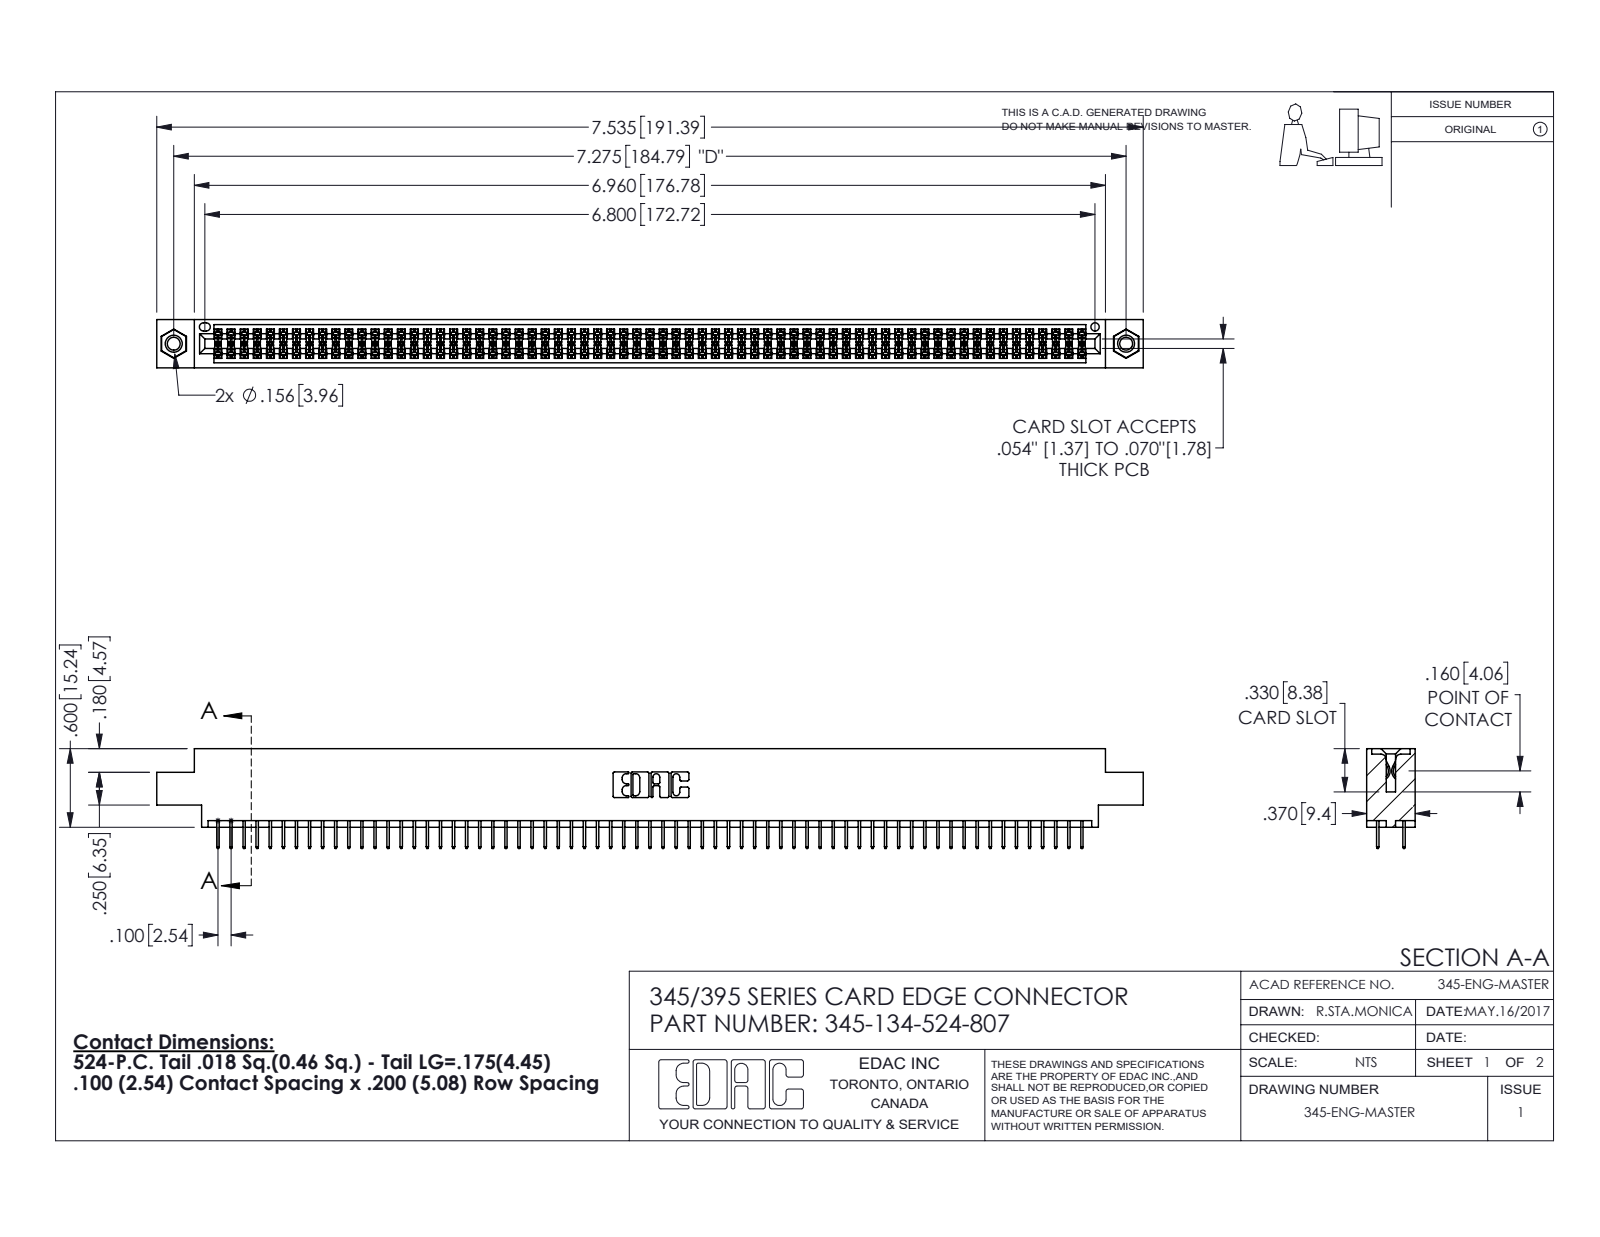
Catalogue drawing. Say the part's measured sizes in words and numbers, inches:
The part is named "345 Part_0.170 Offset - 0.156 Dia-TI; 345-250-001_345-250-005-103; 345-292-001_345-293-124; 345-134-524-807". Its 3-D file was written by "SolidWorks 2016 (CONFIG_CONTROL_DESIGN)". It is 137 solids with 7426 faces: 5342 planar, 2068 cylindrical and 16 other. Overall it measures 7.535 by 0.762 by 0.37 inches. Its volume is 1.129 cubic inches and its surface area 42.56 square inches. Round holes: 2 of diameter 0.098, 2 of diameter 0.125, 2 of diameter 0.156, 1 of diameter 0.064. Round bosses or shafts: 2 of diameter 0.155. Partial cylindrical surfaces (rounded edges, fillets, slot ends): 201 of radius 0.006, 22 of radius 0.01, 6 of radius 0.007, 6 of radius 0.031, 3 of radius 0.026, 2 of radius 0.014, 2 of radius 0.019, 2 of radius 0.022. The main face-to-face distances are 0.072, 0.298, 0.37, 0.2, 0.098, 0.272, 0.025, 0.225, 0.072, 0.175. The hole center spacings are 0.27, 7.039, 7.275.
